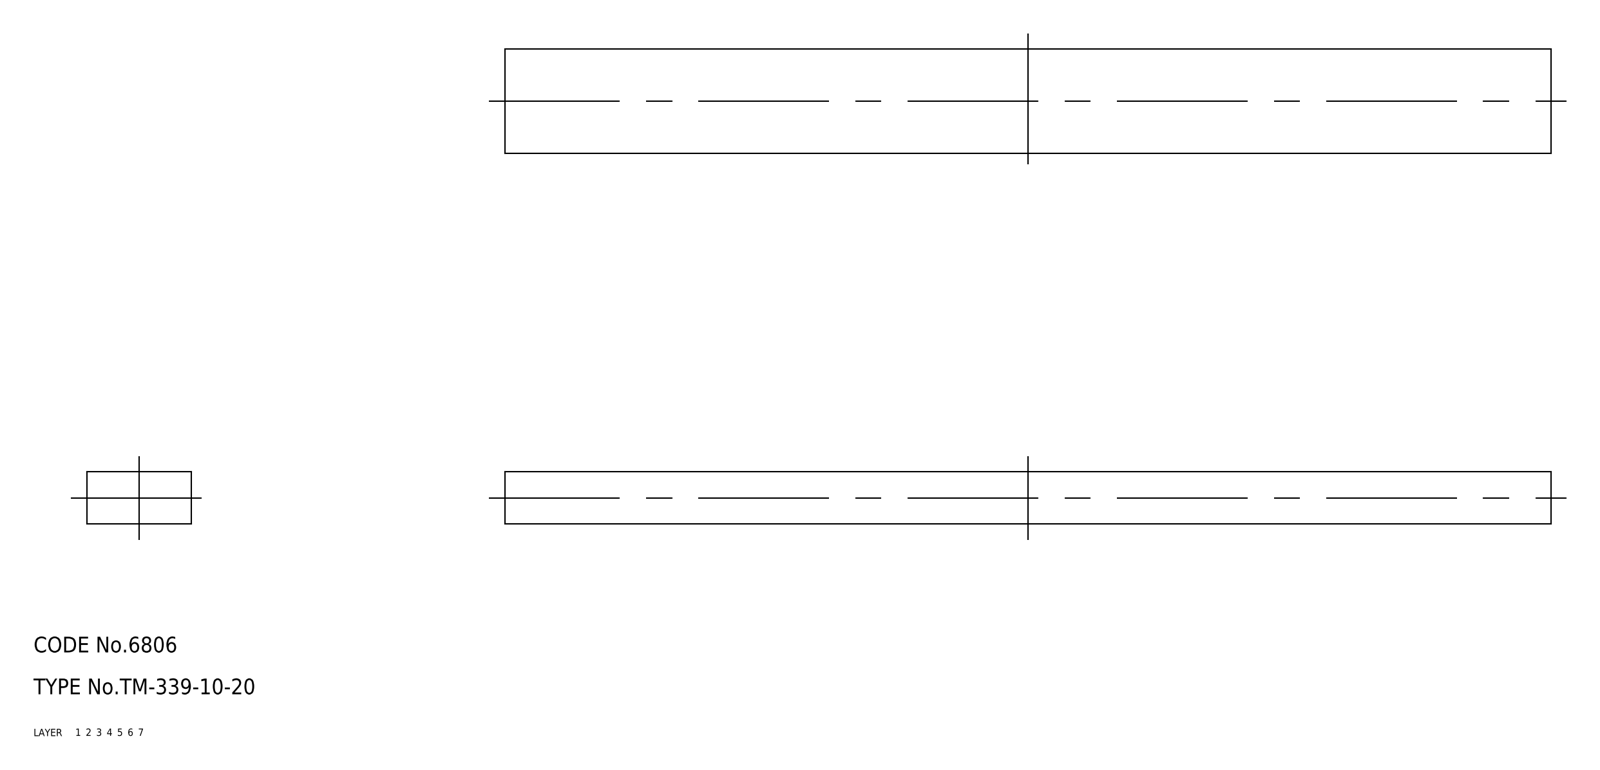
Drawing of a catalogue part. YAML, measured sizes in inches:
part_name: "rubber foam; TM_339_10_20"
step_written_by: "SolidWorks 2015 (AUTOMOTIVE_DESIGN)"
units: inches
bodies: {solids: 1, faces: 6, planar: 6, cylindrical: 0, other: 0}
overall_size: [7.874, 0.787, 0.394]
volume: 2.441
surface_area: 19.22
face_to_face_distances: [0.394, 0.787, 7.874]
